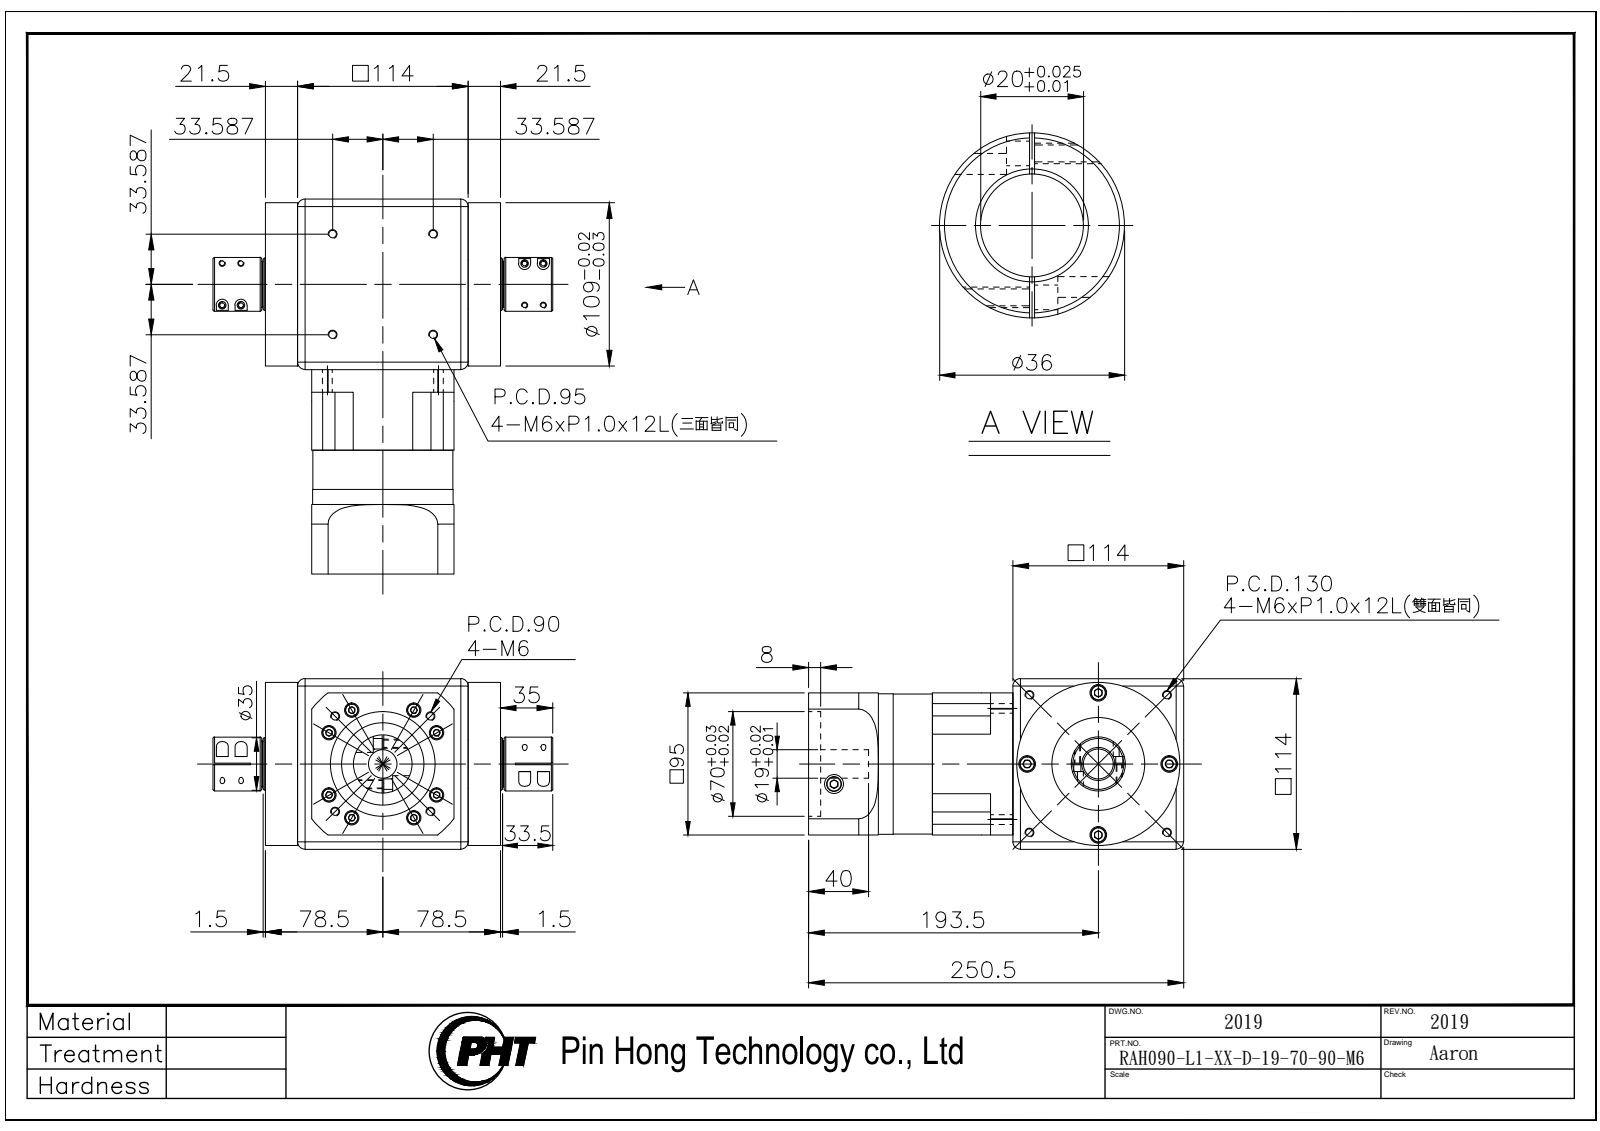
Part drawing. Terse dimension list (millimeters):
name: RAH090-L1-XX-D-19-70-90-M6_2019
written by: SolidWorks 2016 (AUTOMOTIVE_DESIGN)
unit: mm
bodies: 2 solids, 1019 faces (510 planar, 336 cylindrical, 173 other)
size: 250.5 × 227 × 114
volume: 2 814 000 mm³; area: 233 959 mm²
holes: 16× ⌀5, 8× ⌀5.2, 8× ⌀6, 8× ⌀9.5, 4× ⌀6.6, 4× ⌀6.8, 4× ⌀11, 2× ⌀12.7, 1× ⌀19, 1× ⌀20, 1× ⌀27, 1× ⌀28
bosses: 16× ⌀8.5, 8× ⌀10, 8× ⌀9.2, 8× ⌀5, 1× ⌀109, 1× ⌀93.8, 1× ⌀93.5, 1× ⌀80
rounds: 8× R4.75, 4× R2.55, 4× R6, 1× R52, 1× R60, 1× R79.1
face distances: 114, 104.5, 9.5, 31, 95, 126, 21.5, 157, 135.5, 3
hole spacings: 41.5, 67.18, 11.81, 13.05, 16.41, 45.99, 47.5, 52.73
